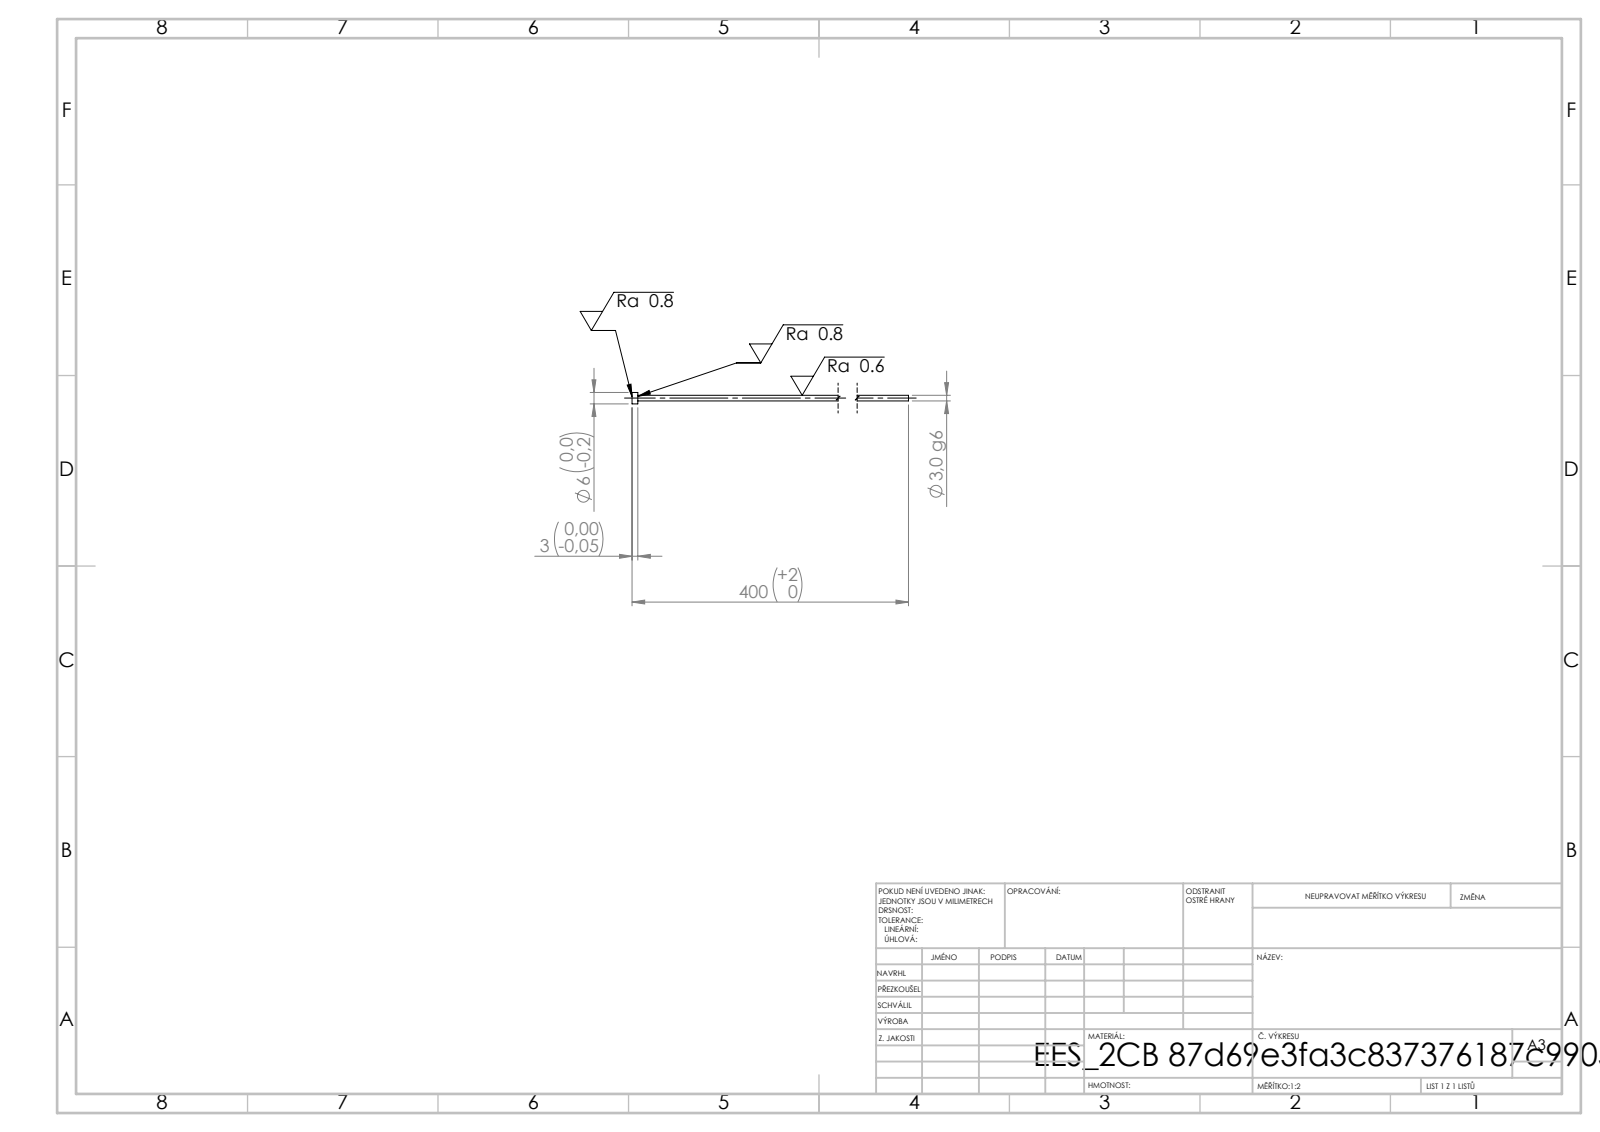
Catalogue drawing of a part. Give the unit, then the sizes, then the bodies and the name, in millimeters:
Units: millimetres
Overall size (bounding box): 400 × 6 × 6
Round bosses / shafts (diameter × count): ⌀6 ×1, ⌀3 ×1
Main face-to-face distances: 3, 400, 397
Volume: 2 891 mm³ · Surface area: 3 855 mm²
Bodies: 1 solid, 7 faces (3 planar, 4 cylindrical, 0 other)
STEP written by: SolidWorks 2019 (CONFIG_CONTROL_DESIGN)
